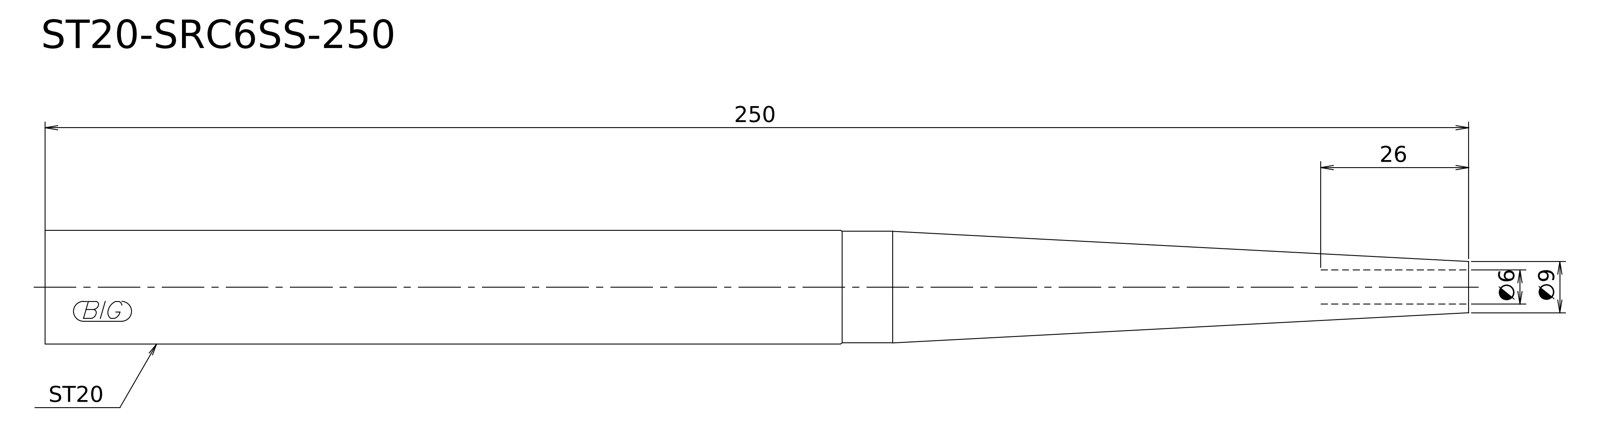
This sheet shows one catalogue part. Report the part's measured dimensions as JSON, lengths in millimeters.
{"step_written_by": "Kubotek KeyCreator V8.5.1 (14335) (CONFIG_CONTROL_DESIGN)", "units": "millimeters", "bodies": {"solids": 1, "faces": 6, "planar": 2, "cylindrical": 2, "other": 2}, "overall_size": [250, 20, 20], "volume_mm3": 63642, "surface_area_mm2": 14273, "round_bosses_or_shafts": [[20, 1], [19.6, 1]], "face_to_face_distances": [250]}
